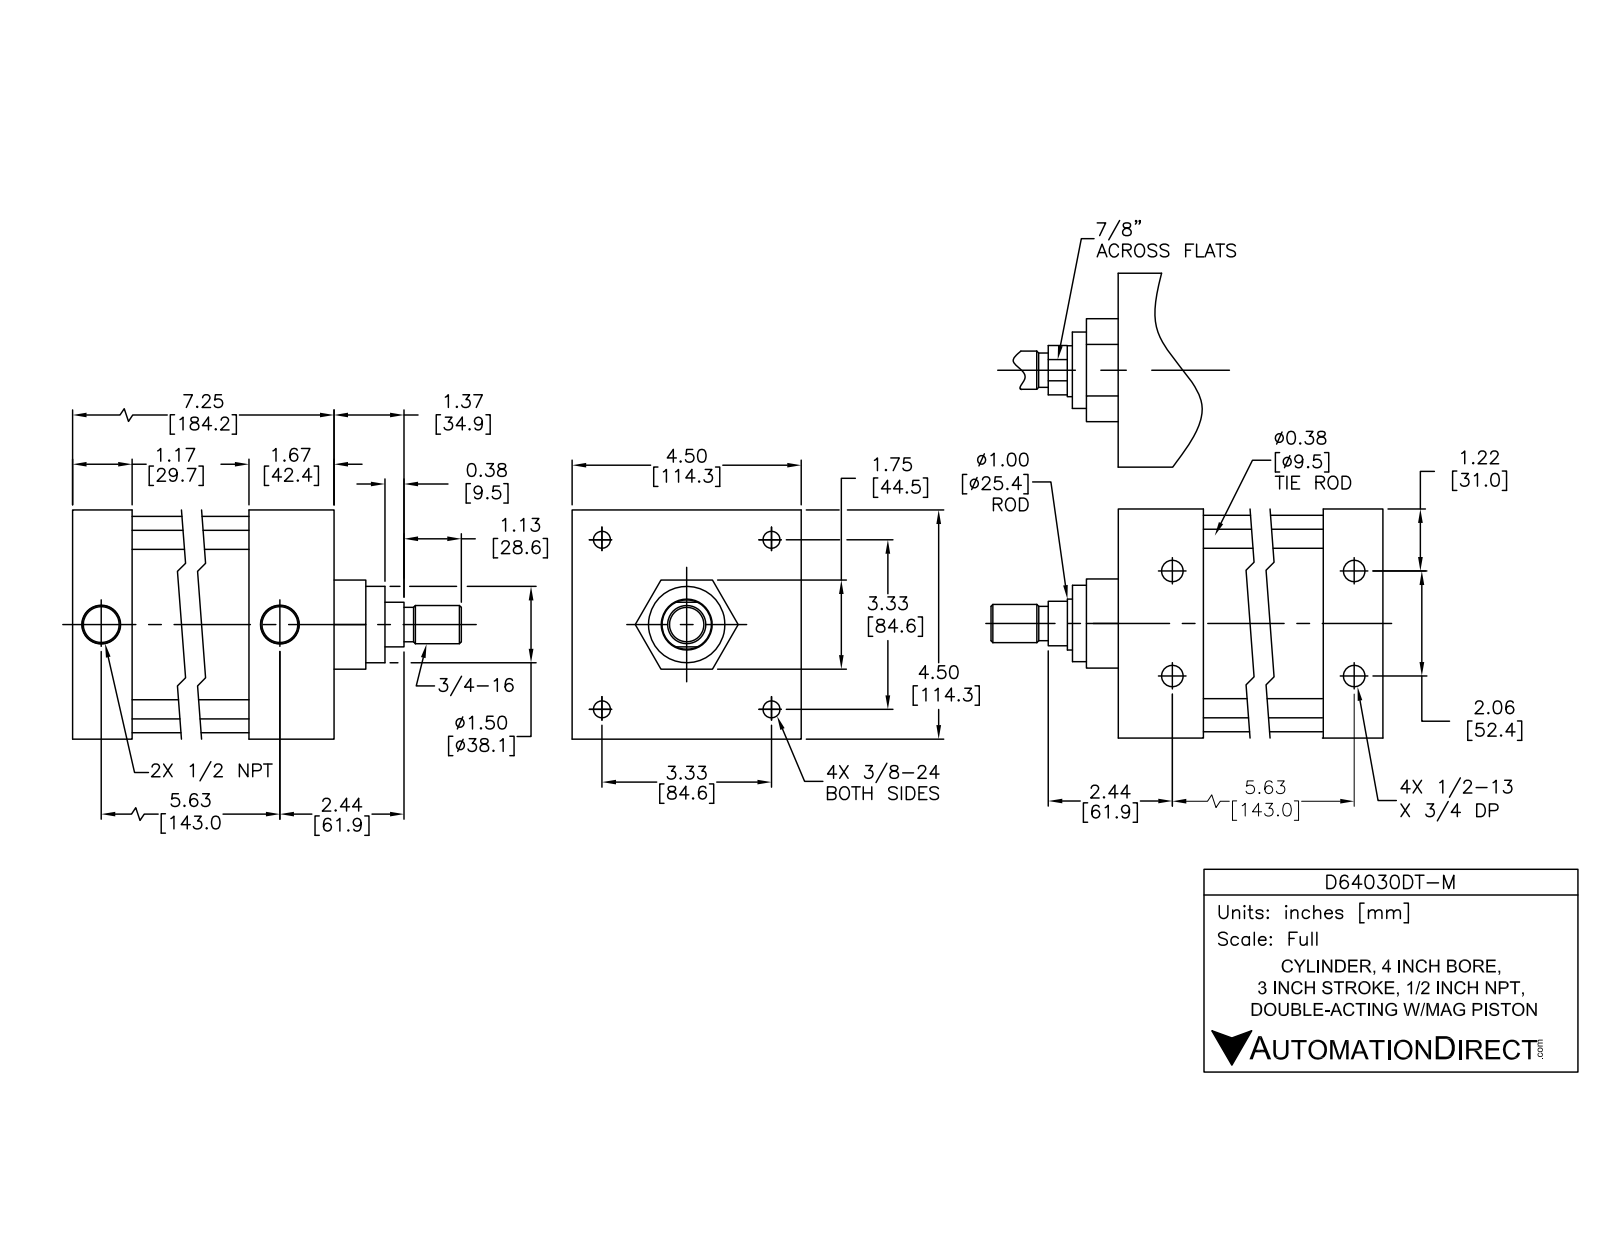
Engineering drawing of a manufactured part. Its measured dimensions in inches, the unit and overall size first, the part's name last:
Units: inches
Overall size (bounding box): 9.745 × 4.5 × 4.5
Round holes (diameter × count): ⌀0.33 ×4, ⌀0.406 ×4, ⌀0.417 ×4, ⌀0.625 ×4, ⌀0.5 ×2, ⌀0.766 ×2, ⌀1 ×1, ⌀1.003 ×1, ⌀4 ×1
Round bosses / shafts (diameter × count): ⌀0.609 ×4, ⌀0.375 ×4, ⌀0.34 ×4, ⌀4.25 ×1, ⌀3.997 ×1, ⌀1.75 ×1, ⌀0.997 ×1, ⌀0.97 ×1
Partial cylindrical surfaces — rounded edges, fillets, slot ends (radius × count): R0.45 ×4
Main face-to-face distances: 4.5, 0.08, 4.326, 7.246, 1.75, 5.997, 1.249, 4.751, 1.246, 2.495
Hole centre spacings: 1.031, 2.349, 3.322, 5.716, 5.622, 2.062, 4.698, 5.988
Volume: 85.63 in³ · Surface area: 390.3 in²
Bodies: 12 solids, 303 faces (99 planar, 114 cylindrical, 90 other)
Part name (STEP PRODUCT): D64030DT-M BODY; D64030DT-M; D64030DT-M PISTON
STEP written by: SolidWorks 2015 (AUTOMOTIVE_DESIGN)
